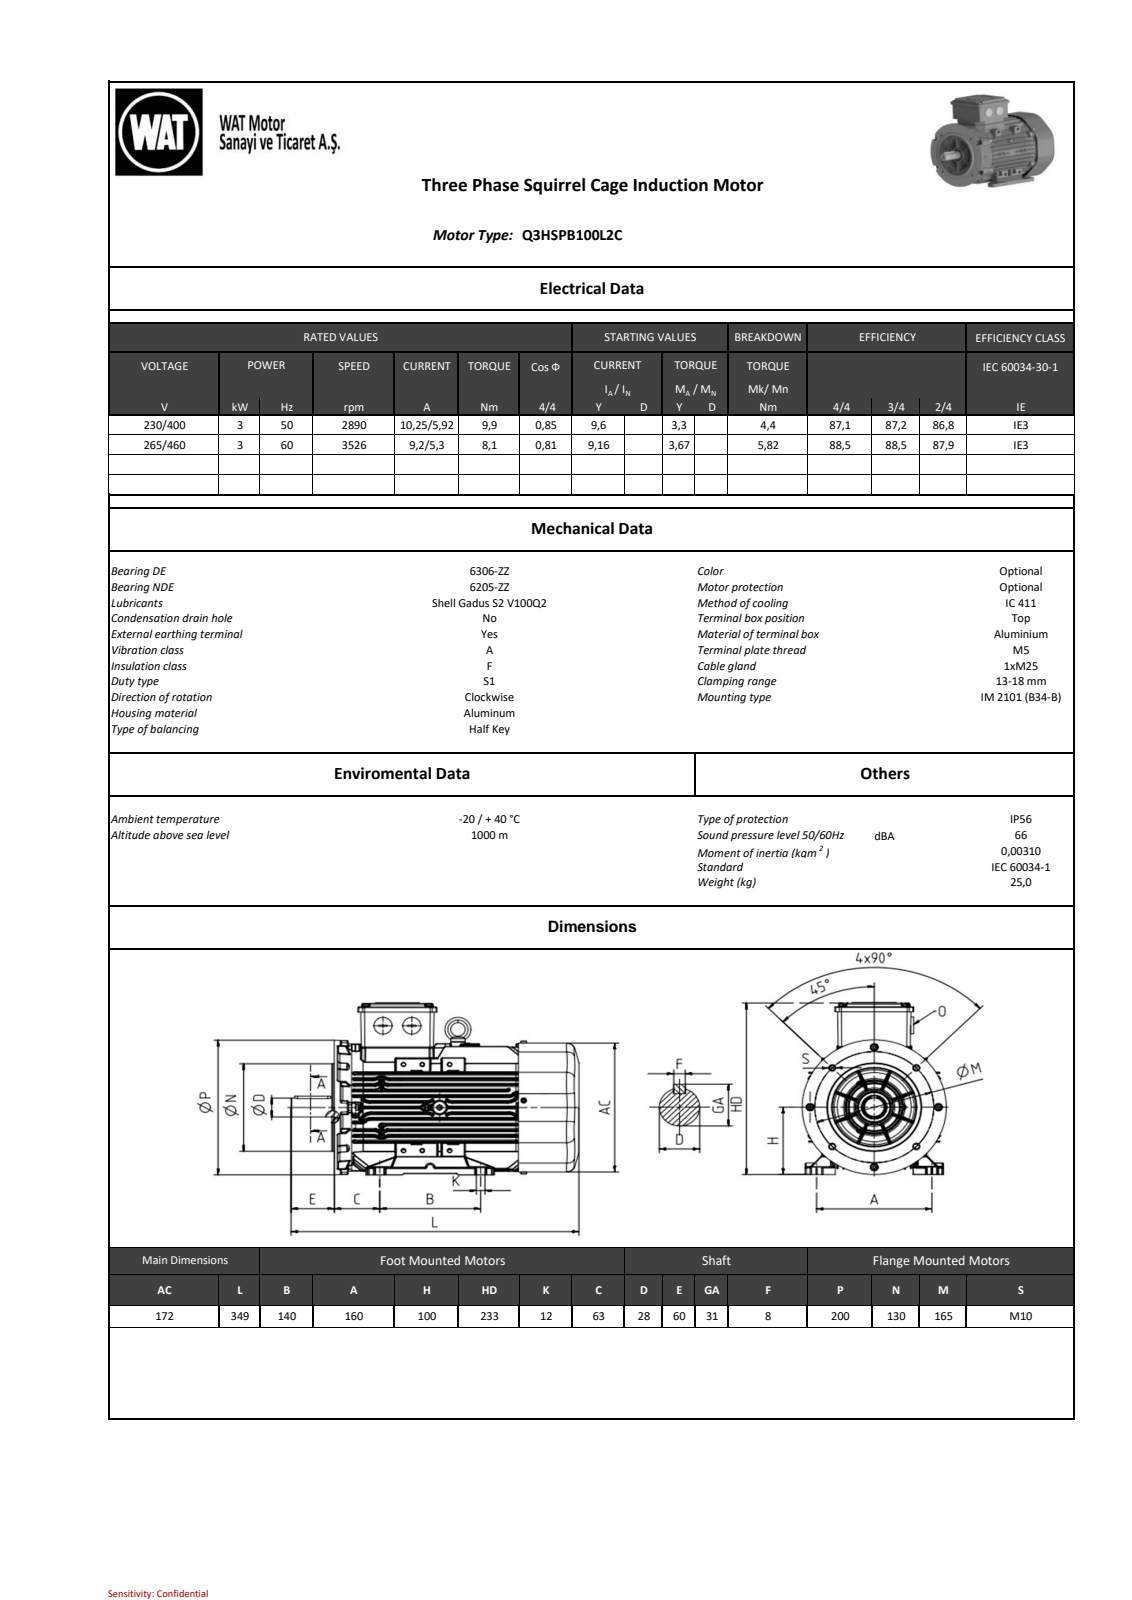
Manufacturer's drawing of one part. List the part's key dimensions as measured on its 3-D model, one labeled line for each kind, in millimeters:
Part name (STEP PRODUCT): QHS Series_ 100_B34b_stp_objects
STEP written by: SIEMENS PLM Software NX2206.8101 (AUTOMOTIVE_DESIGN)
Units: millimetres
Bodies: 0 solids, 6870 faces (1649 planar, 3039 cylindrical, 2182 other)
Overall size (bounding box): 349.04 × 233.22 × 200.35
Round holes (diameter × count): ⌀9 ×4, ⌀3.5 ×3, ⌀9.87 ×1, ⌀79.79 ×1, ⌀97.79 ×1, ⌀115.78 ×1
Round bosses / shafts (diameter × count): ⌀8 ×7, ⌀5 ×4, ⌀25 ×2, ⌀130 ×1, ⌀102.19 ×1, ⌀84.19 ×1, ⌀30 ×1, ⌀28 ×1
Partial cylindrical surfaces — rounded edges, fillets, slot ends (radius × count): R1 ×741, R0.8 ×522, R0.5 ×361, R2 ×184, R0.7 ×72, R8 ×28, R4 ×10, R1.6 ×8
Main face-to-face distances: 7.5, 91.91, 82.98, 8.93, 23.57, 206, 7.37, 50.35, 90.35, 16.87
Hole centre spacings: 116.68, 67.56, 82.47, 82.54, 165.01, 38.97, 38.99, 39.05
